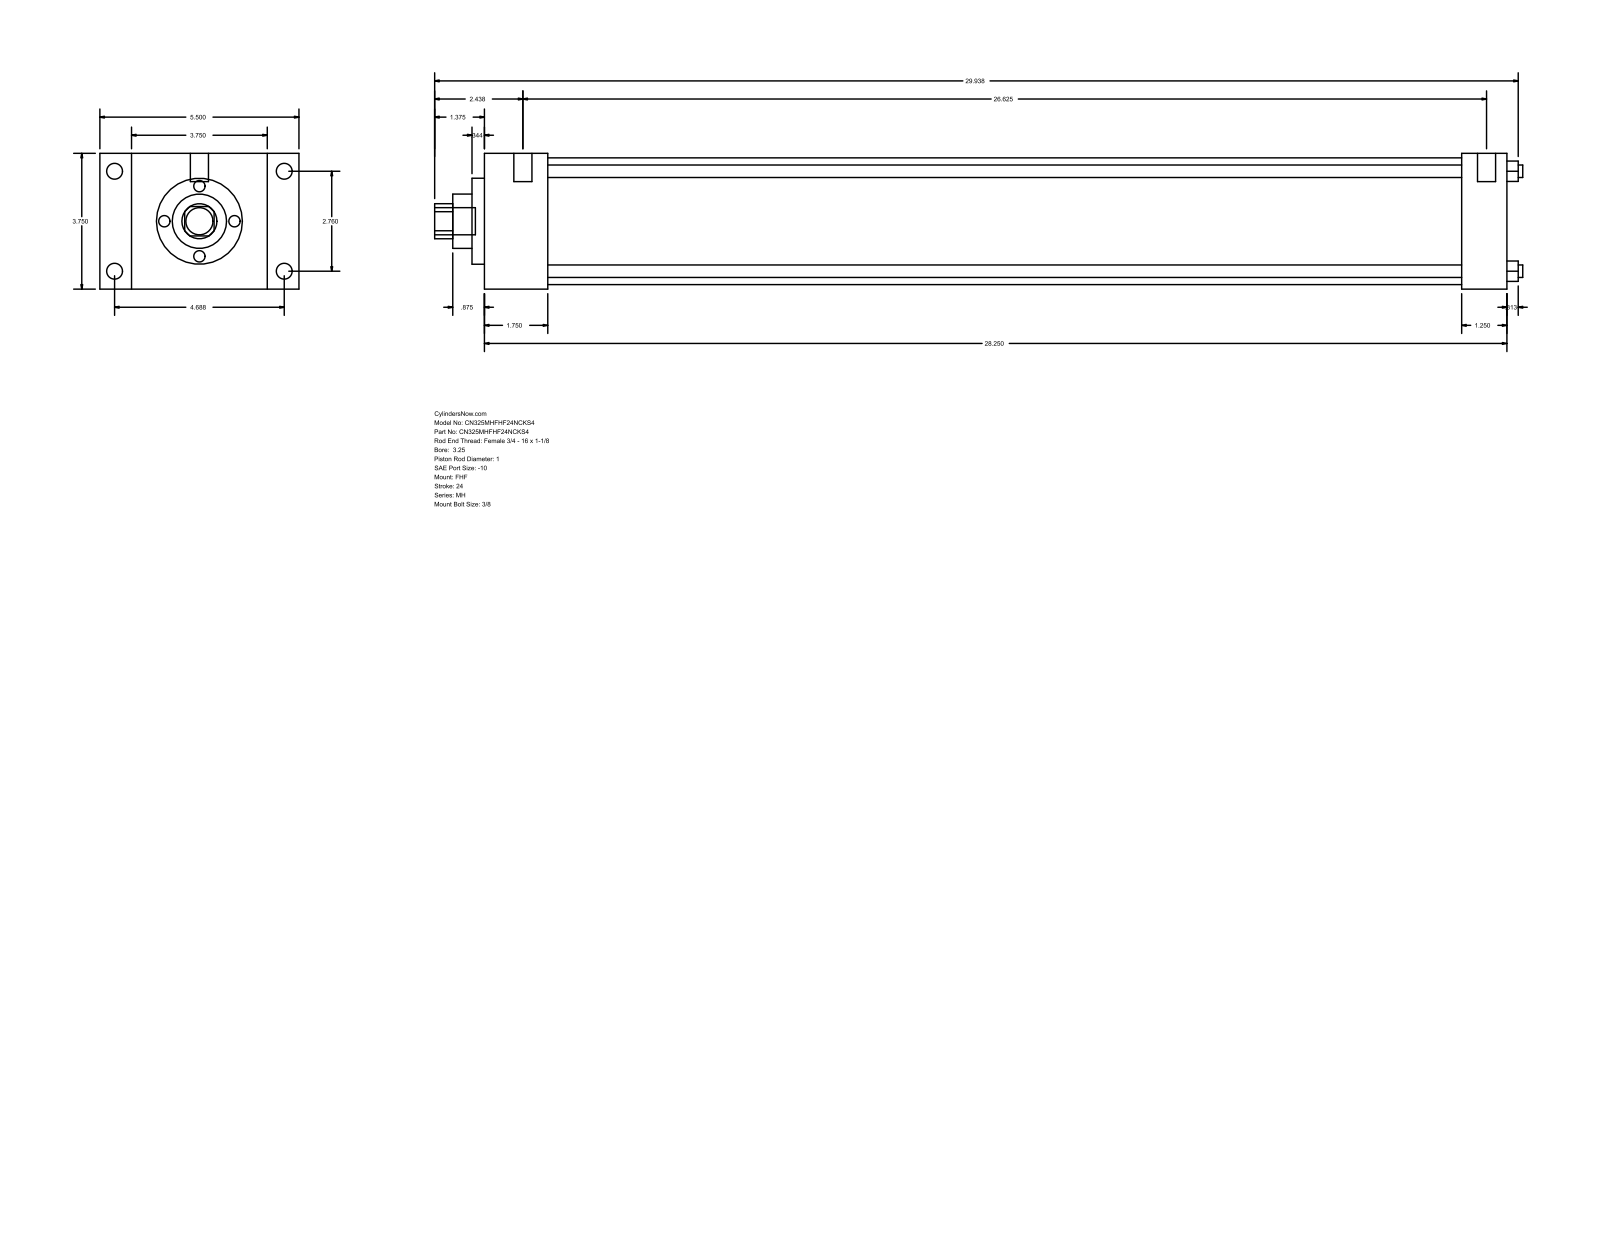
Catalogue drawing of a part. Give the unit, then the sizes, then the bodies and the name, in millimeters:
Units: millimetres
Overall size (bounding box): 763.59 × 139.7 × 95.25
Round holes (diameter × count): ⌀8.76 ×4, ⌀25.4 ×1, ⌀38.1 ×1, ⌀60.33 ×1, ⌀88.9 ×1
Round bosses / shafts (diameter × count): ⌀11.13 ×4, ⌀5.56 ×4, ⌀12.7 ×2, ⌀19.05 ×1
Partial cylindrical surfaces — rounded edges, fillets, slot ends (radius × count): R12.29 ×1
Main face-to-face distances: 95.24, 717.56, 44.46, 673.1, 22.23, 117.47, 139.7, 685.81, 641.35, 31.75
Hole centre spacings: 49.57, 70.1, 99.14
Bodies: 0 solids, 90 faces (61 planar, 29 cylindrical, 0 other)
Part name (STEP PRODUCT): MH_FHF__0325_1
STEP written by: GSSL Pune (CONFIG_CONTROL_DESIGN)
